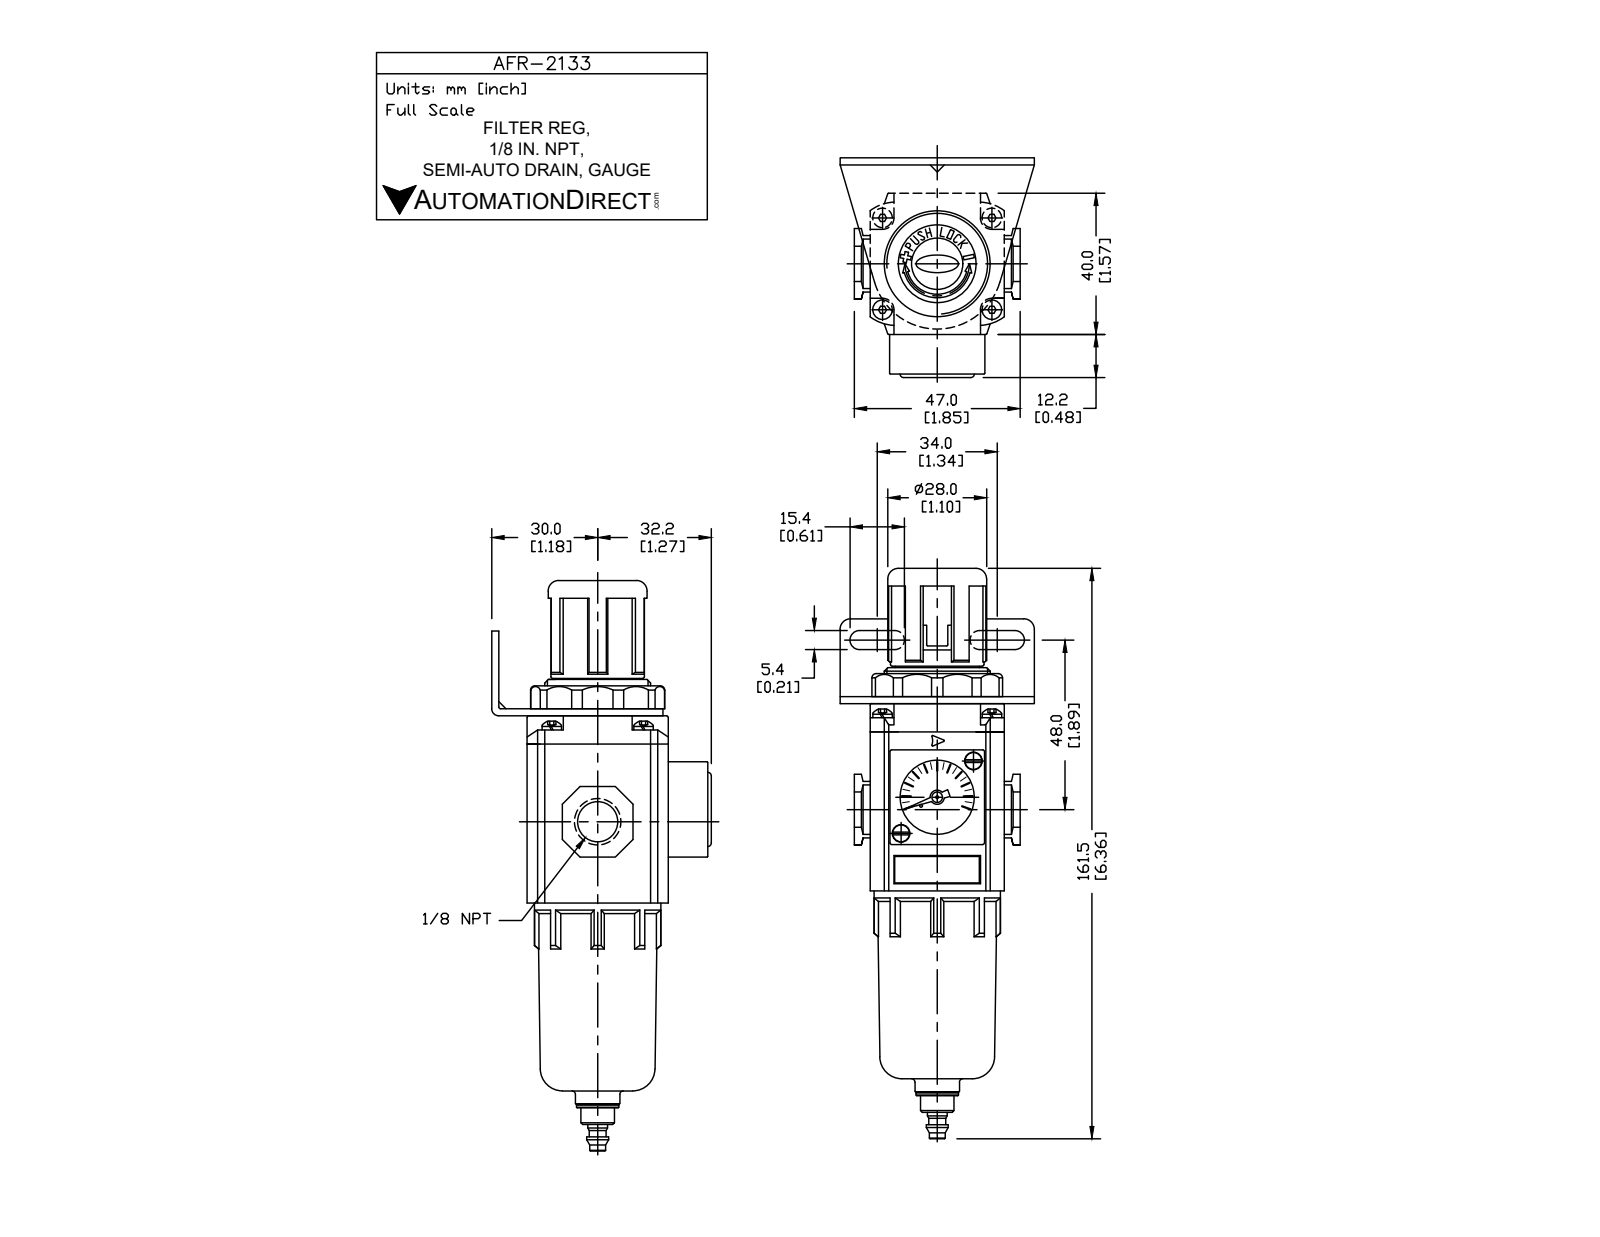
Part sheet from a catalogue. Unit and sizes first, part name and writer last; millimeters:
Units: millimetres
Overall size (bounding box): 161.2 × 62 × 55
Round holes (diameter × count): ⌀3 ×7, ⌀2 ×1, ⌀8.43 ×1, ⌀21 ×1, ⌀22 ×1, ⌀25.5 ×1, ⌀30 ×1
Round bosses / shafts (diameter × count): ⌀5.5 ×4, ⌀2.7 ×2, ⌀28 ×1, ⌀26 ×1, ⌀23.8 ×1, ⌀14 ×1, ⌀12.6 ×1, ⌀12 ×1
Partial cylindrical surfaces — rounded edges, fillets, slot ends (radius × count): R1 ×12, R1.2 ×10, R3.25 ×6, R0.3 ×4, R2.75 ×4, R12 ×4, R0.2 ×3, R2 ×1
Main face-to-face distances: 2, 55, 40, 53, 38, 39, 10, 1, 50, 11
Hole centre spacings: 20.23, 14.5, 26, 31, 40.46, 28.99
Volume: 135 089 mm³ · Surface area: 40 067 mm²
Bodies: 15 solids, 548 faces (329 planar, 159 cylindrical, 60 other)
Part name (STEP PRODUCT): AFR-2133
STEP written by: SolidWorks 2015 (CONFIG_CONTROL_DESIGN)
